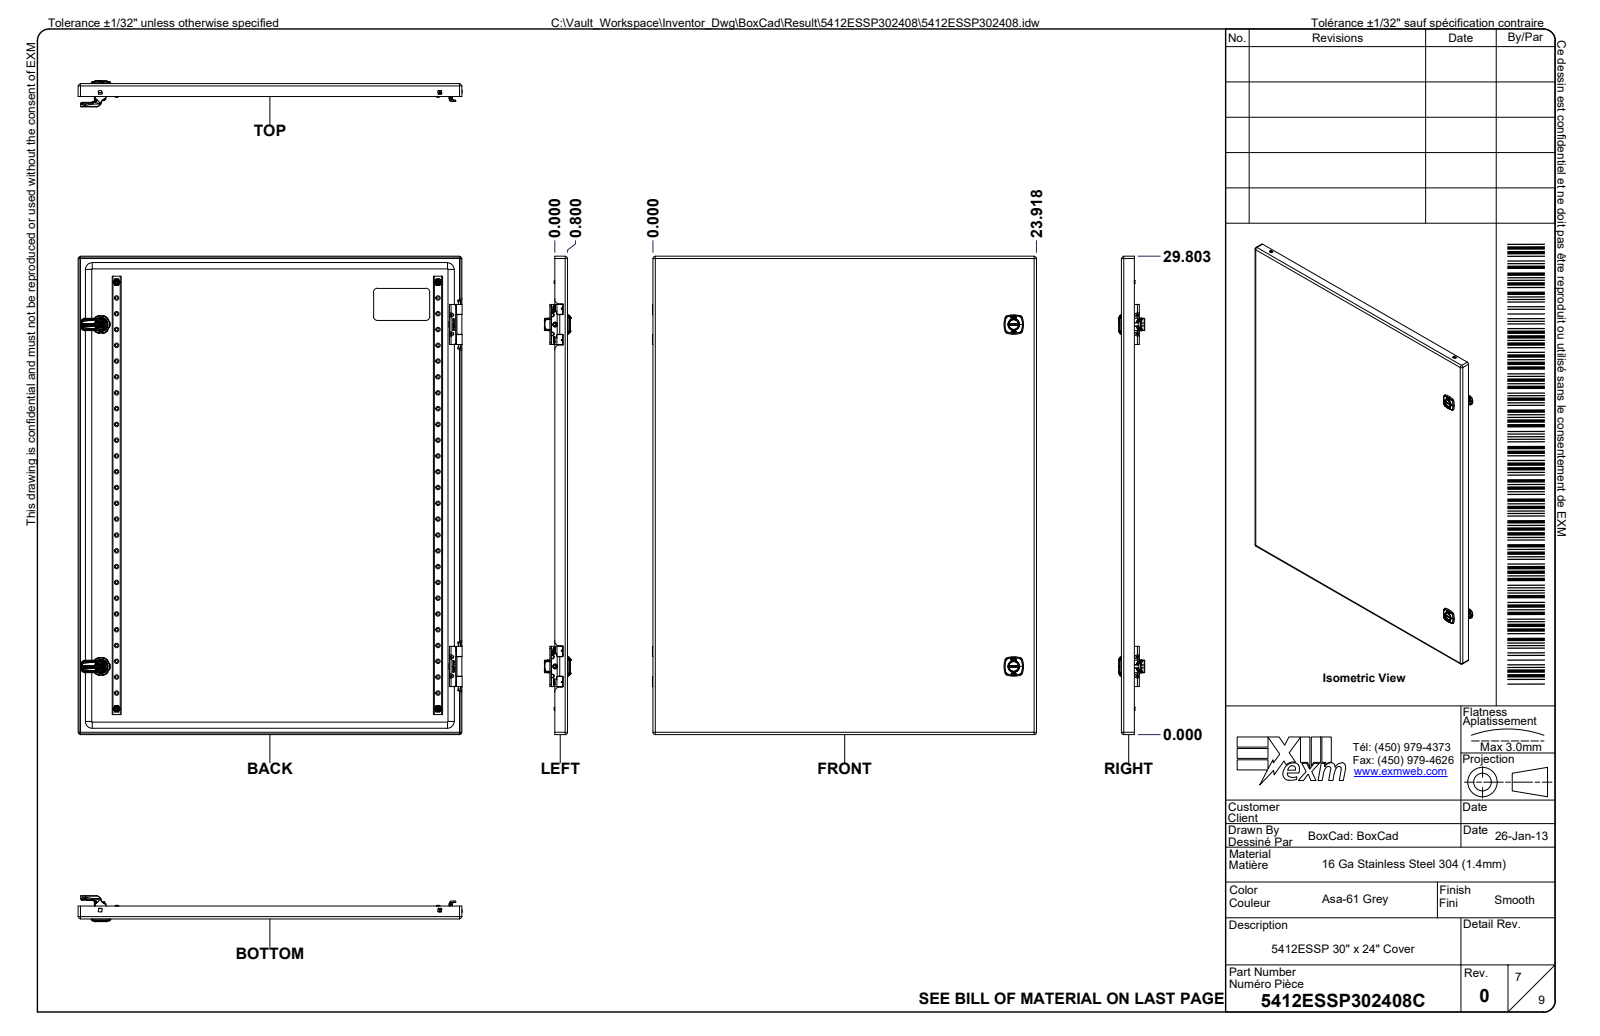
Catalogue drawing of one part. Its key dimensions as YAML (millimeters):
part_name: "5412ESSP302408; 5412ESSP302408B; 5412ESSP302408B-P; STK-Q-16020 (+8 more)"
step_written_by: "Autodesk Inventor 2024 (AUTOMOTIVE_DESIGN)"
units: millimeters
bodies: {solids: 64, faces: 9418, planar: 3065, cylindrical: 2015, other: 4338}
overall_size: [762, 609.6, 236.4]
volume: 3597000
surface_area: 4423000
round_holes:
  - {diameter: 4.2, count: 52}
  - {diameter: 0.8, count: 9}
  - {diameter: 5.1, count: 8}
  - {diameter: 8, count: 8}
  - {diameter: 7.4, count: 6}
  - {diameter: 7.9, count: 6}
  - {diameter: 1.1, count: 4}
  - {diameter: 5, count: 4}
  - {diameter: 6.8, count: 4}
  - {diameter: 6.9, count: 4}
  - {diameter: 9.9, count: 4}
  - {diameter: 6, count: 2}
round_bosses_or_shafts:
  - {diameter: 6, count: 52}
  - {diameter: 5.9, count: 9}
  - {diameter: 0.8, count: 9}
  - {diameter: 1, count: 8}
  - {diameter: 18.2, count: 4}
  - {diameter: 9.5, count: 4}
  - {diameter: 7.9, count: 4}
  - {diameter: 6.7, count: 4}
partial_cylinders:
  - {radius: 0.5, count: 106}
  - {radius: 0.2, count: 68}
  - {radius: 1, count: 66}
  - {radius: 0.3, count: 34}
  - {radius: 0.8, count: 34}
  - {radius: 0.3, count: 28}
  - {radius: 2.1, count: 24}
  - {radius: 3.2, count: 20}
face_to_face_distances: [1.3, 230.7, 229.3, 232, 23.5, 22.2, 207.1, 208.5, 2.7, 26.2]
hole_center_spacings: [25, 50, 75, 100, 125, 150, 175, 200]
